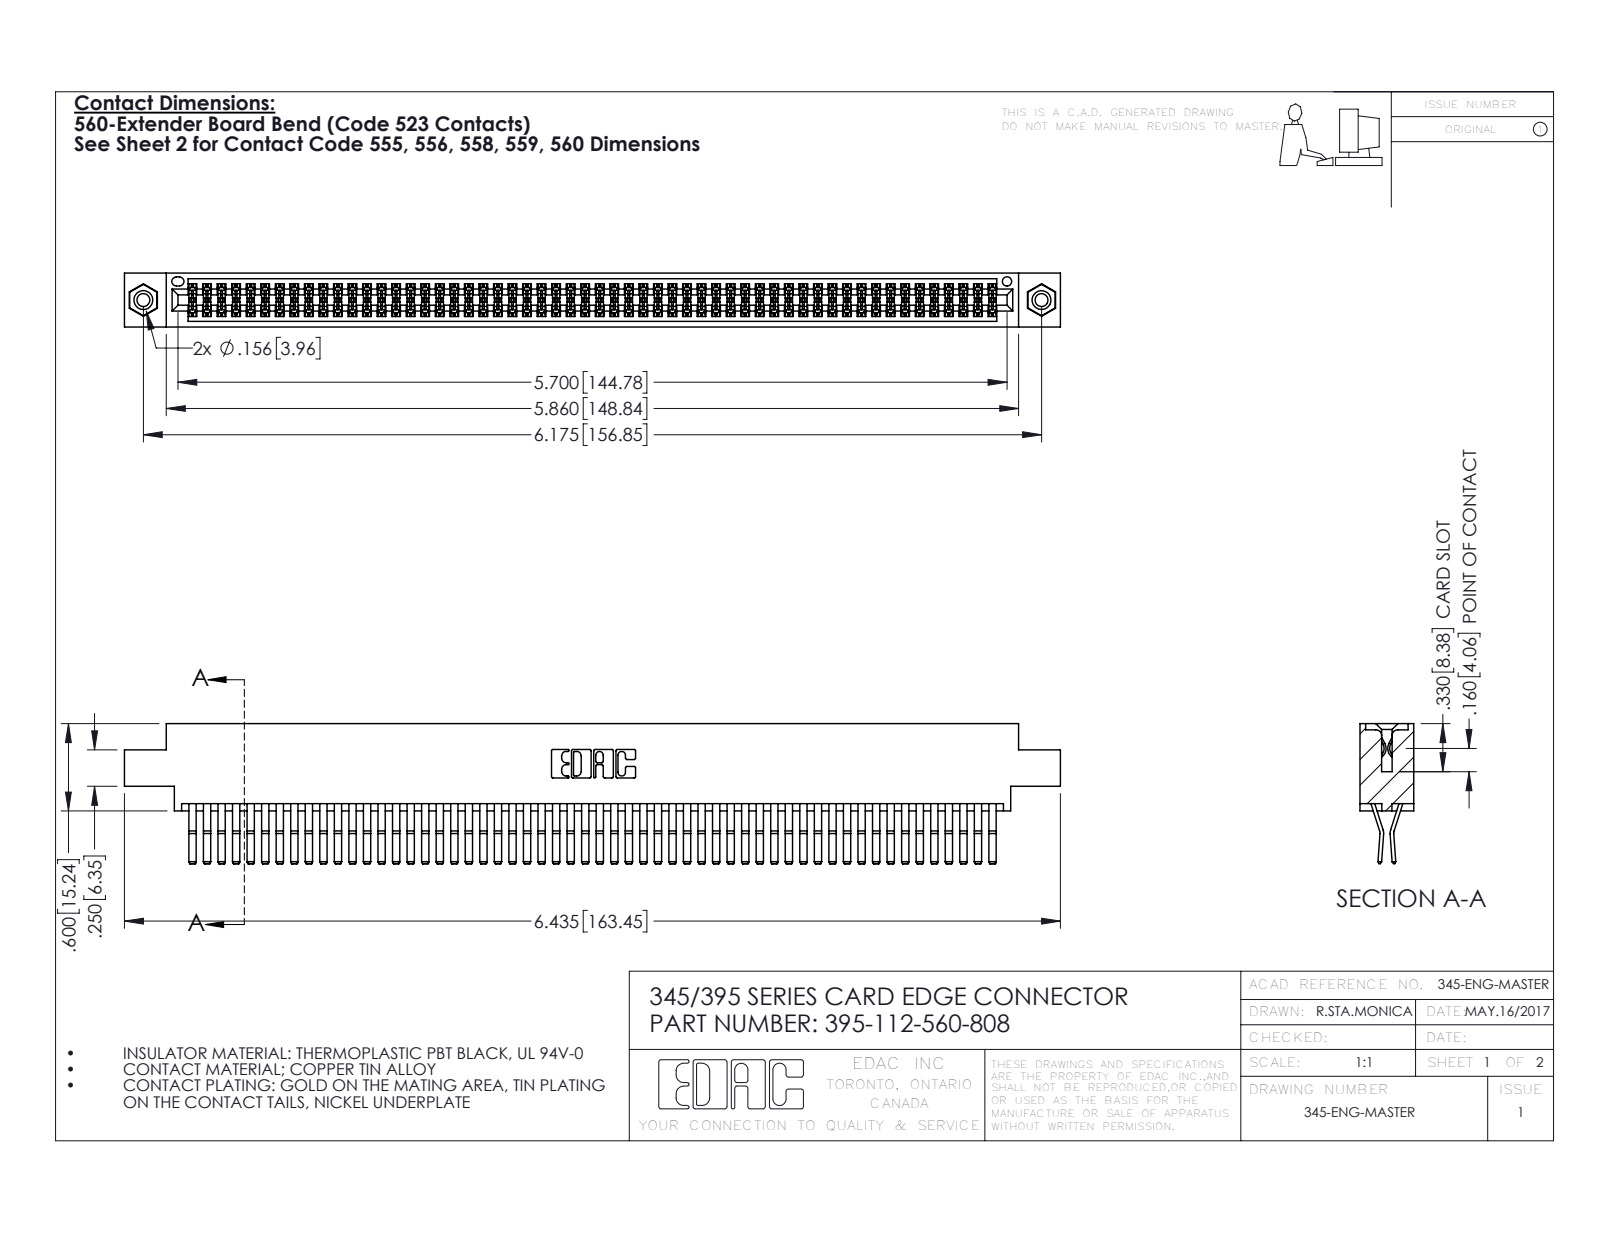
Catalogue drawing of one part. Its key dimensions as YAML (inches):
part_name: "345-250-001_345-250-003-102; 345-292-001_560 Tail; 395-112-560-808; 345 Part_0.170 Offset - 0.156 Dia-TI"
step_written_by: "SolidWorks 2016 (CONFIG_CONTROL_DESIGN)"
units: inches
bodies: {solids: 115, faces: 6014, planar: 3812, cylindrical: 2186, other: 16}
overall_size: [6.435, 0.962, 0.37]
volume: 1.014
surface_area: 41.67
round_holes:
  - {diameter: 0.089, count: 2}
  - {diameter: 0.125, count: 2}
  - {diameter: 0.156, count: 2}
  - {diameter: 0.064, count: 1}
round_bosses_or_shafts:
  - {diameter: 0.155, count: 2}
partial_cylinders:
  - {radius: 0.006, count: 168}
  - {radius: 0.01, count: 22}
  - {radius: 0.007, count: 6}
  - {radius: 0.031, count: 6}
  - {radius: 0.026, count: 3}
  - {radius: 0.01, count: 2}
  - {radius: 0.014, count: 2}
  - {radius: 0.019, count: 2}
face_to_face_distances: [0.025, 0.072, 0.298, 0.37, 0.2, 0.098, 0.272, 0.225, 0.175, 0.149]
hole_center_spacings: [0.27, 5.939, 6.175]
